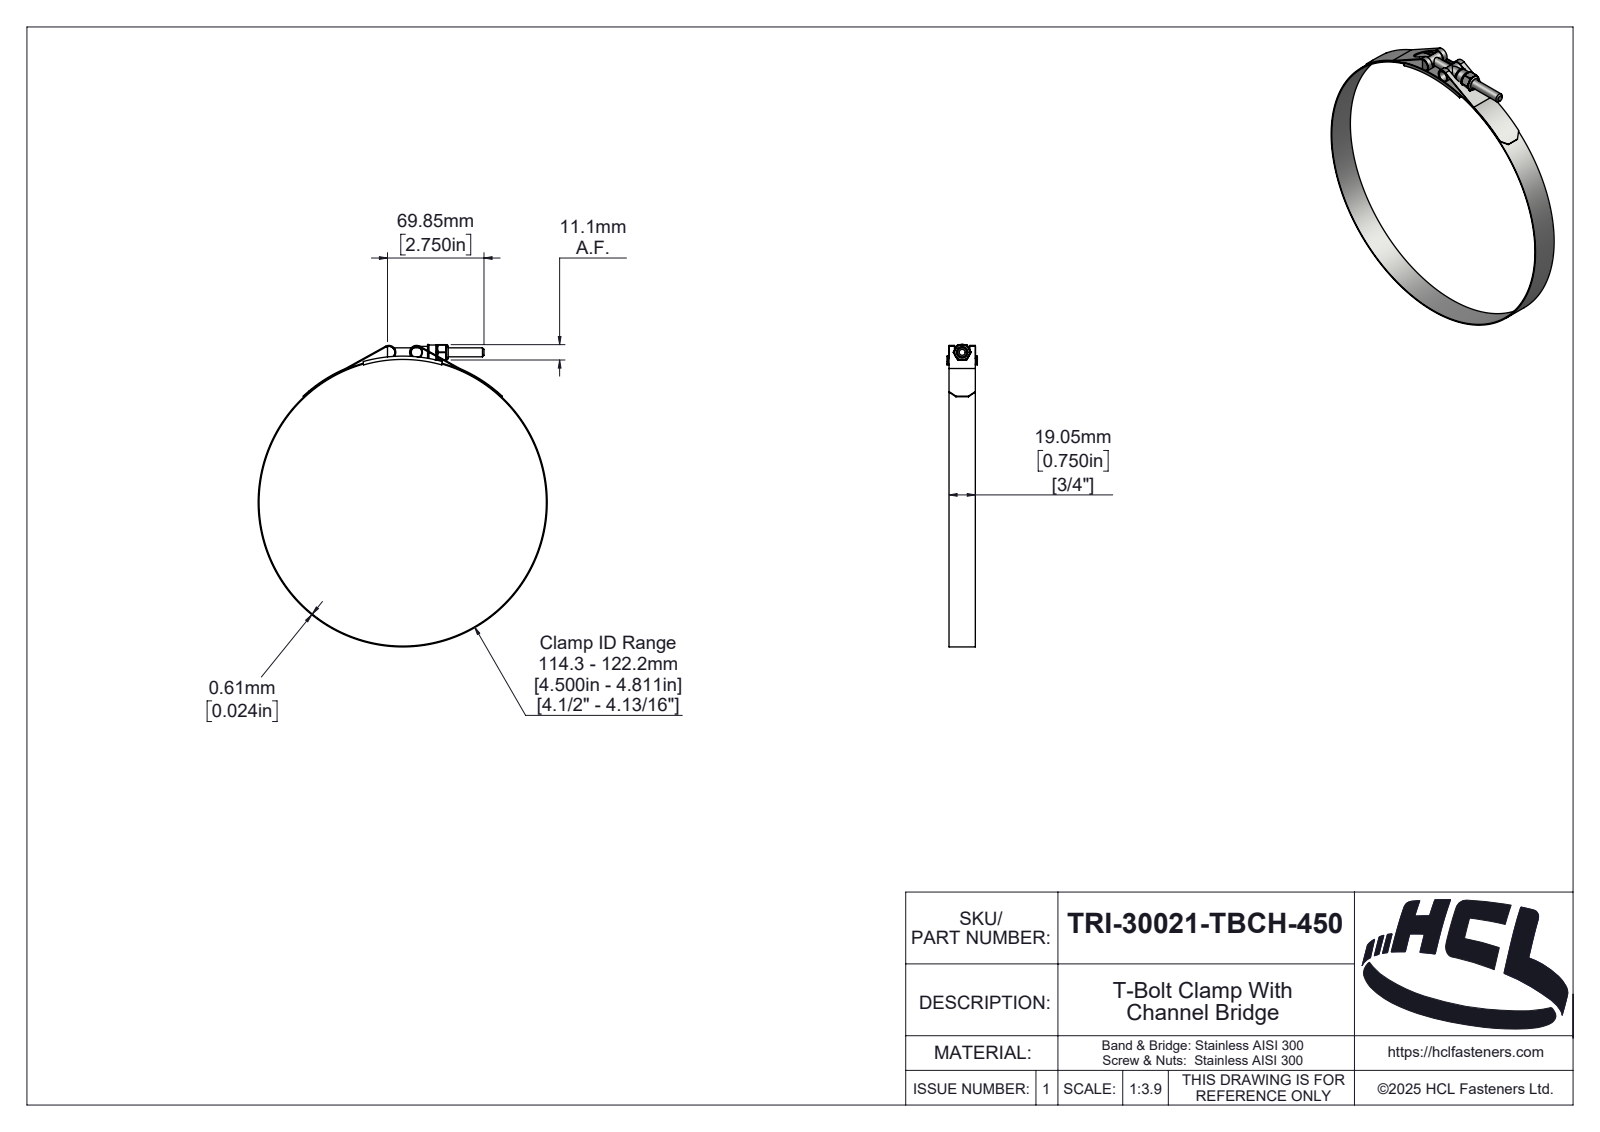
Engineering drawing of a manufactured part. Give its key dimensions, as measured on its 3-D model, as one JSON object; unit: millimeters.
{"part_name": "TRI-30021-TBCH-450", "step_written_by": "SolidWorks 2025 (AUTOMOTIVE_DESIGN)", "units": "millimeters", "bodies": {"solids": 6, "faces": 330, "planar": 46, "cylindrical": 122, "other": 162}, "overall_size": [218.87, 209.22, 22], "volume_mm3": 14053, "surface_area_mm2": 37890, "round_holes": [[5.4, 1], [6.35, 1], [6.5, 1], [7.58, 1], [208, 1]], "round_bosses_or_shafts": [[8.58, 2], [209.22, 1], [10.58, 1]], "partial_cylinders_radius": [[0.39, 6], [0.5, 2], [4.39, 2], [5, 2], [0.59, 1], [2.42, 1], [3.03, 1], [3.19, 1]], "face_to_face_distances": [0.61, 19.06, 1.47, 20.53, 21.39, 0.86, 19.92, 0.74, 22, 11.12], "hole_center_spacings": [109]}
